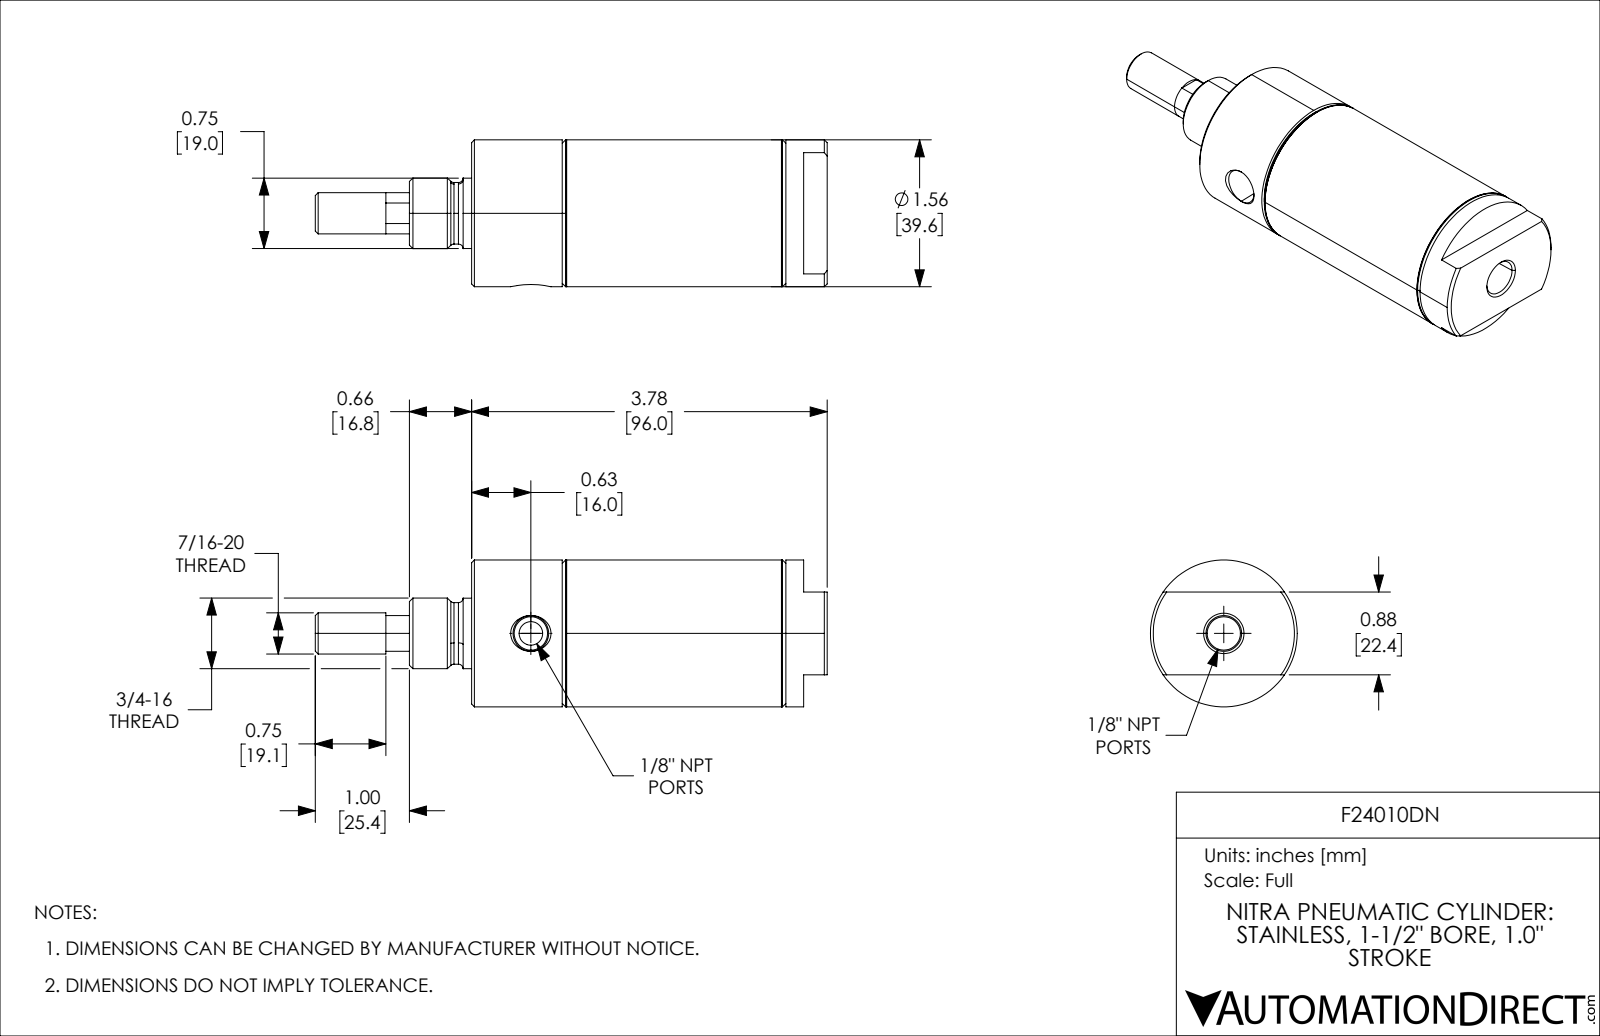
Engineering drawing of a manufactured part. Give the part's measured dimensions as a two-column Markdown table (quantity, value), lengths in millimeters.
| quantity | value |
| --- | --- |
| part name | F24010DN_5; F24010DN_7; F24010DN_9; F24010DN_3 (+1 more) |
| STEP written by | SolidWorks 2021 (CONFIG_CONTROL_DESIGN) |
| units | millimeters |
| bodies | 4 solids, 126 faces (28 planar, 42 cylindrical, 56 other) |
| overall size | 138.12 × 39.62 × 39.62 |
| volume | 90 374 mm³ |
| surface area | 38 603 mm² |
| round holes (diameter × count) | 6.35 × 1, 11.73 × 1, 24.71 × 1, 36.36 × 1 |
| round bosses / shafts (diameter × count) | 39.62 × 1, 38.39 × 1, 19.05 × 1, 18.99 × 1, 16.6 × 1, 11.13 × 1, 11.11 × 1 |
| main face-to-face distances | 22.22, 6.35, 25.4, 11.13, 47.62, 30.86, 56.26, 78.48, 95.96, 65.1 |
